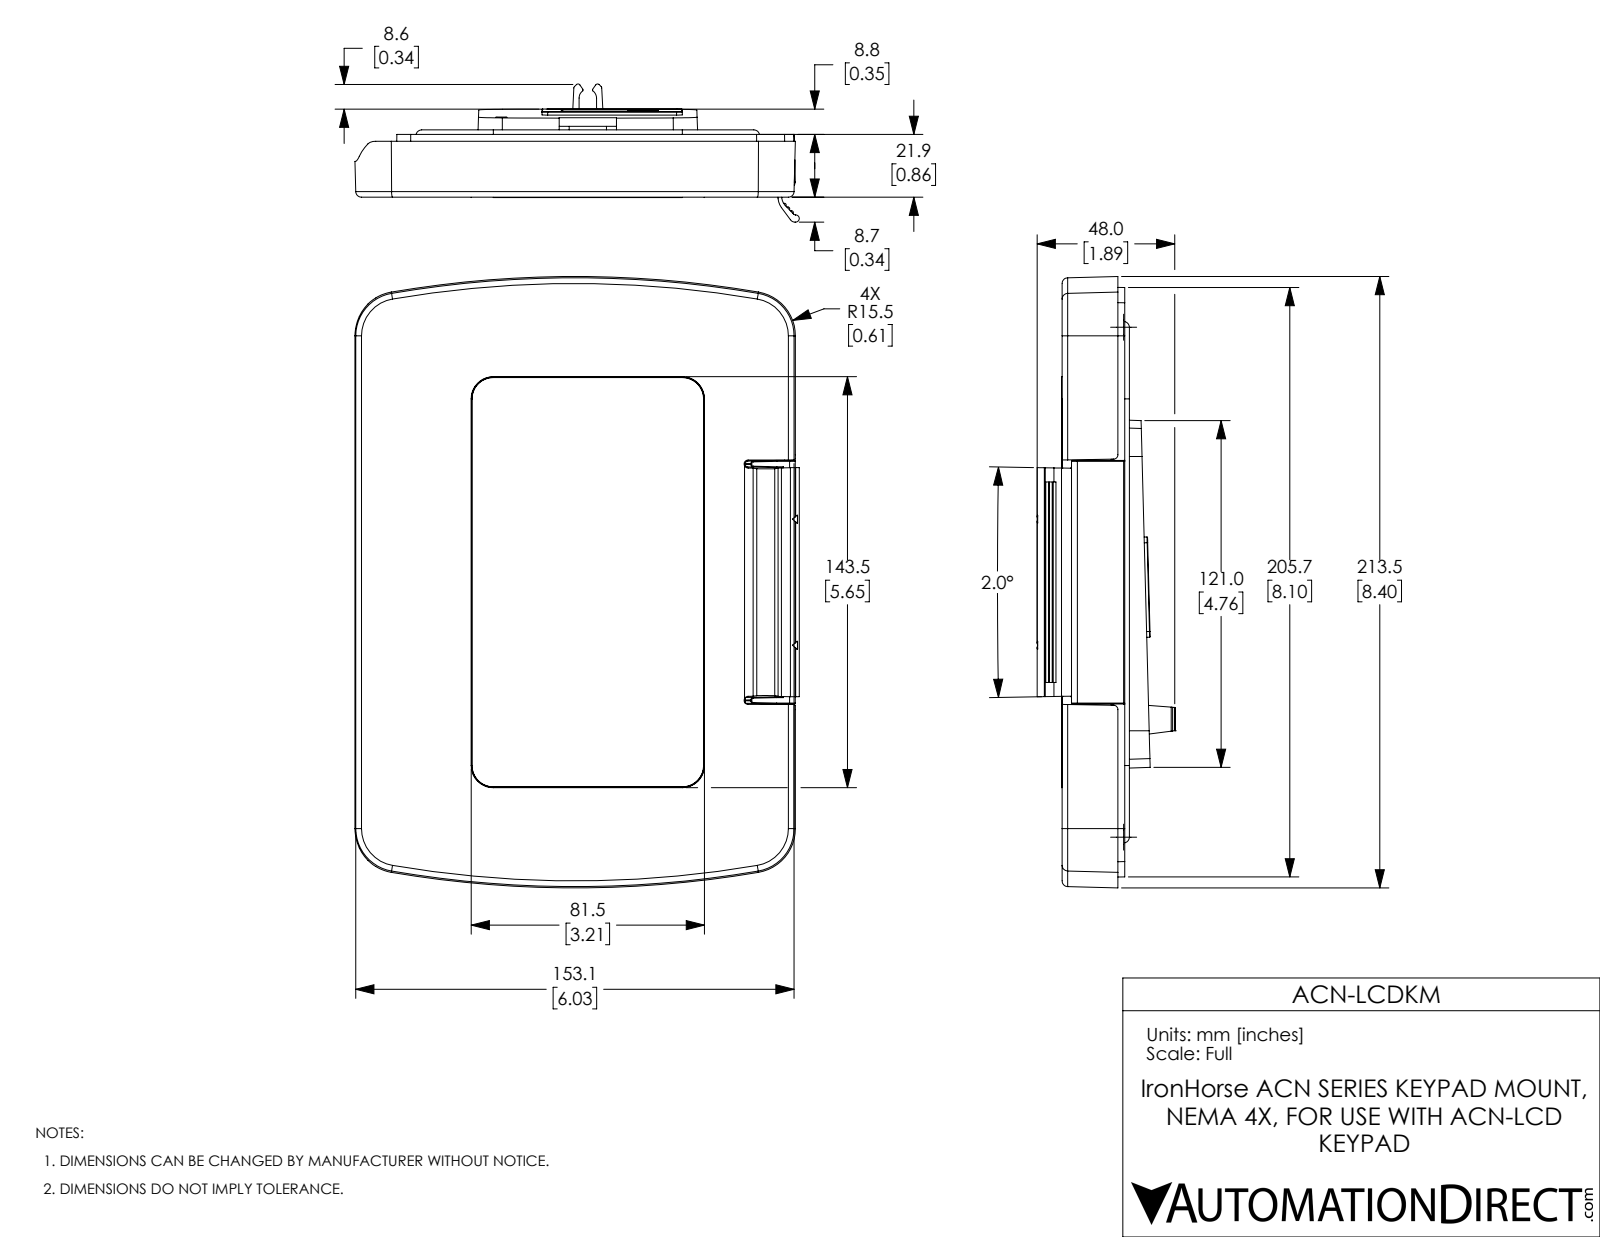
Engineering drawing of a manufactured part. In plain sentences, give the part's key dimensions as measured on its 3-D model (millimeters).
The part is named "LCD LOADER,MOUNT,NEMA-4X,SV-IS7 fIGS fXT Ext1 Red1 r1nc". Its 3-D file was written by "SolidWorks 2017 (AUTOMOTIVE_DESIGN)". It is 6 solids with 2545 faces: 1044 planar, 1229 cylindrical and 272 other. Overall it measures 213.5 by 155.2 by 48.2 millimeters. Its volume is 323 500 cubic millimeters and its surface area 221 700 square millimeters. Round holes: 4 of diameter 4, 4 of diameter 6, 2 of diameter 2, 1 of diameter 4.2. Round bosses or shafts: 6 of diameter 10, 5 of diameter 4, 4 of diameter 3, 3 of diameter 6, 2 of diameter 5. Partial cylindrical surfaces (rounded edges, fillets, slot ends): 40 of radius 0.2, 20 of radius 0.5, 15 of radius 0.1, 15 of radius 0.3, 12 of radius 2, 11 of radius 1, 7 of radius 3, 6 of radius 0.9. The main face-to-face distances are 4, 3, 14, 17, 18, 13.5, 21, 0.5, 3.5, 3.1. The hole center spacings are 73.2, 115.1, 84, 146, 168.4, 5, 5.5, 6.2.
